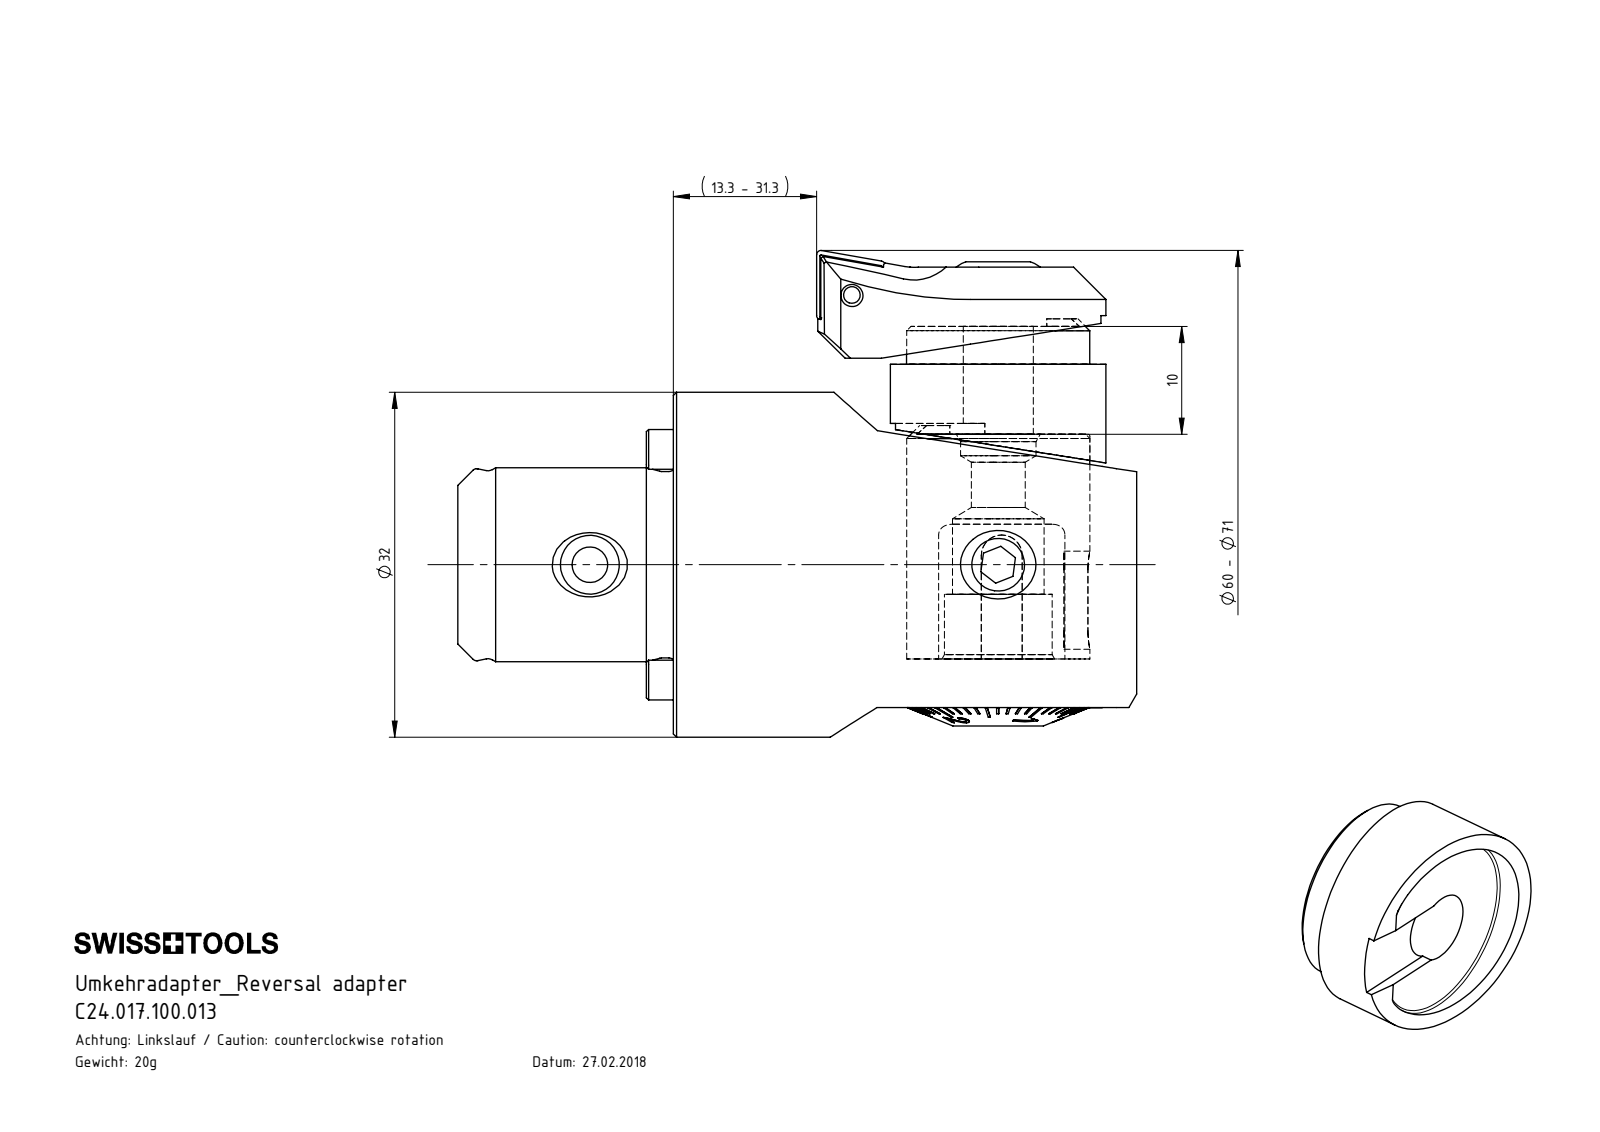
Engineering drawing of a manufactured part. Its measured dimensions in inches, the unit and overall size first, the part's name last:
Units: inches
Overall size (bounding box): 0.787 × 0.787 × 0.526
Round holes (diameter × count): ⌀0.256 ×1, ⌀0.669 ×1
Round bosses / shafts (diameter × count): ⌀0.787 ×1
Partial cylindrical surfaces — rounded edges, fillets, slot ends (radius × count): R0.02 ×2
Main face-to-face distances: 0.394, 0.256, 0.138, 0.039, 0.217, 0.354, 0.421, 0.382, 0.165, 0.028
Volume: 0.157 in³ · Surface area: 2.306 in²
Bodies: 1 solid, 27 faces (11 planar, 11 cylindrical, 5 other)
Part name (STEP PRODUCT): C24.017.100.013; F32-U00.001.010_B
STEP written by: SolidWorks 2017 (CONFIG_CONTROL_DESIGN)
